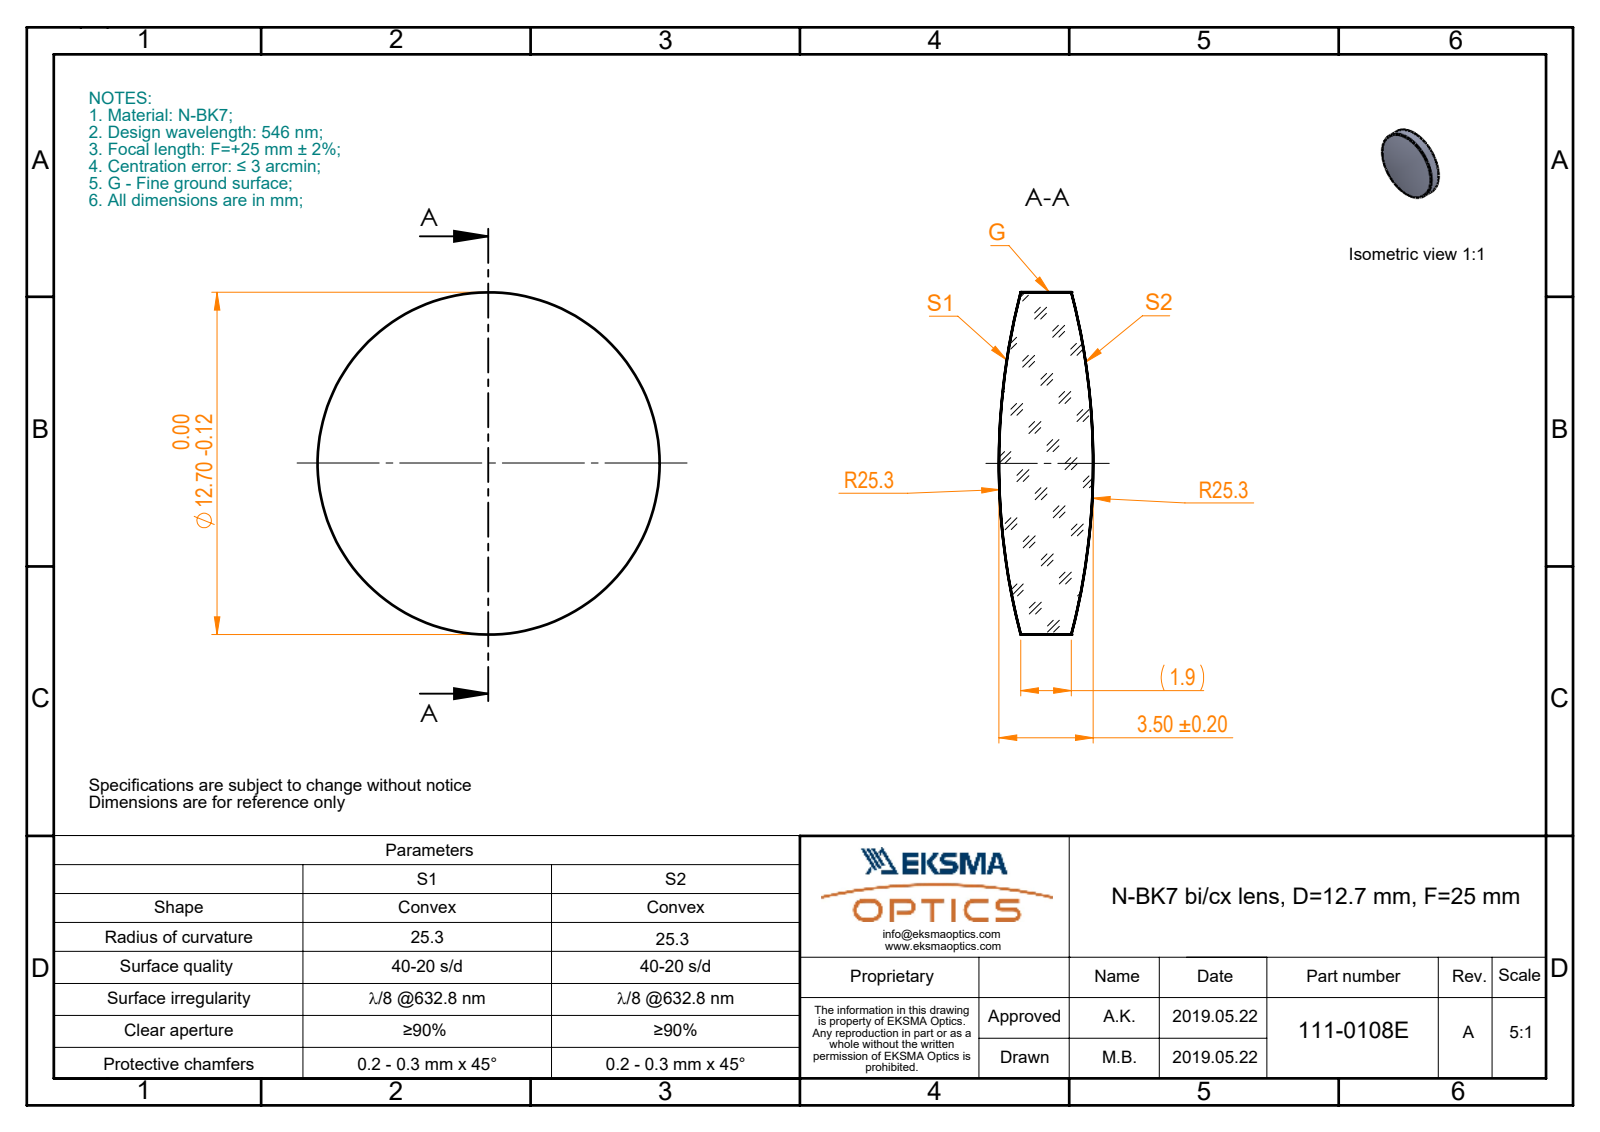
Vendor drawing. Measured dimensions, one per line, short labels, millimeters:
name: 111-0108E BK7 bi-cx 12.7 F25
written by: SolidWorks 2017 (CONFIG_CONTROL_DESIGN)
unit: mm
bodies: 1 solid, 6 faces (0 planar, 2 cylindrical, 4 other)
size: 12.7 × 12.7 × 3.5
volume: 341 mm³; area: 333 mm²
bosses: 1× ⌀12.7
